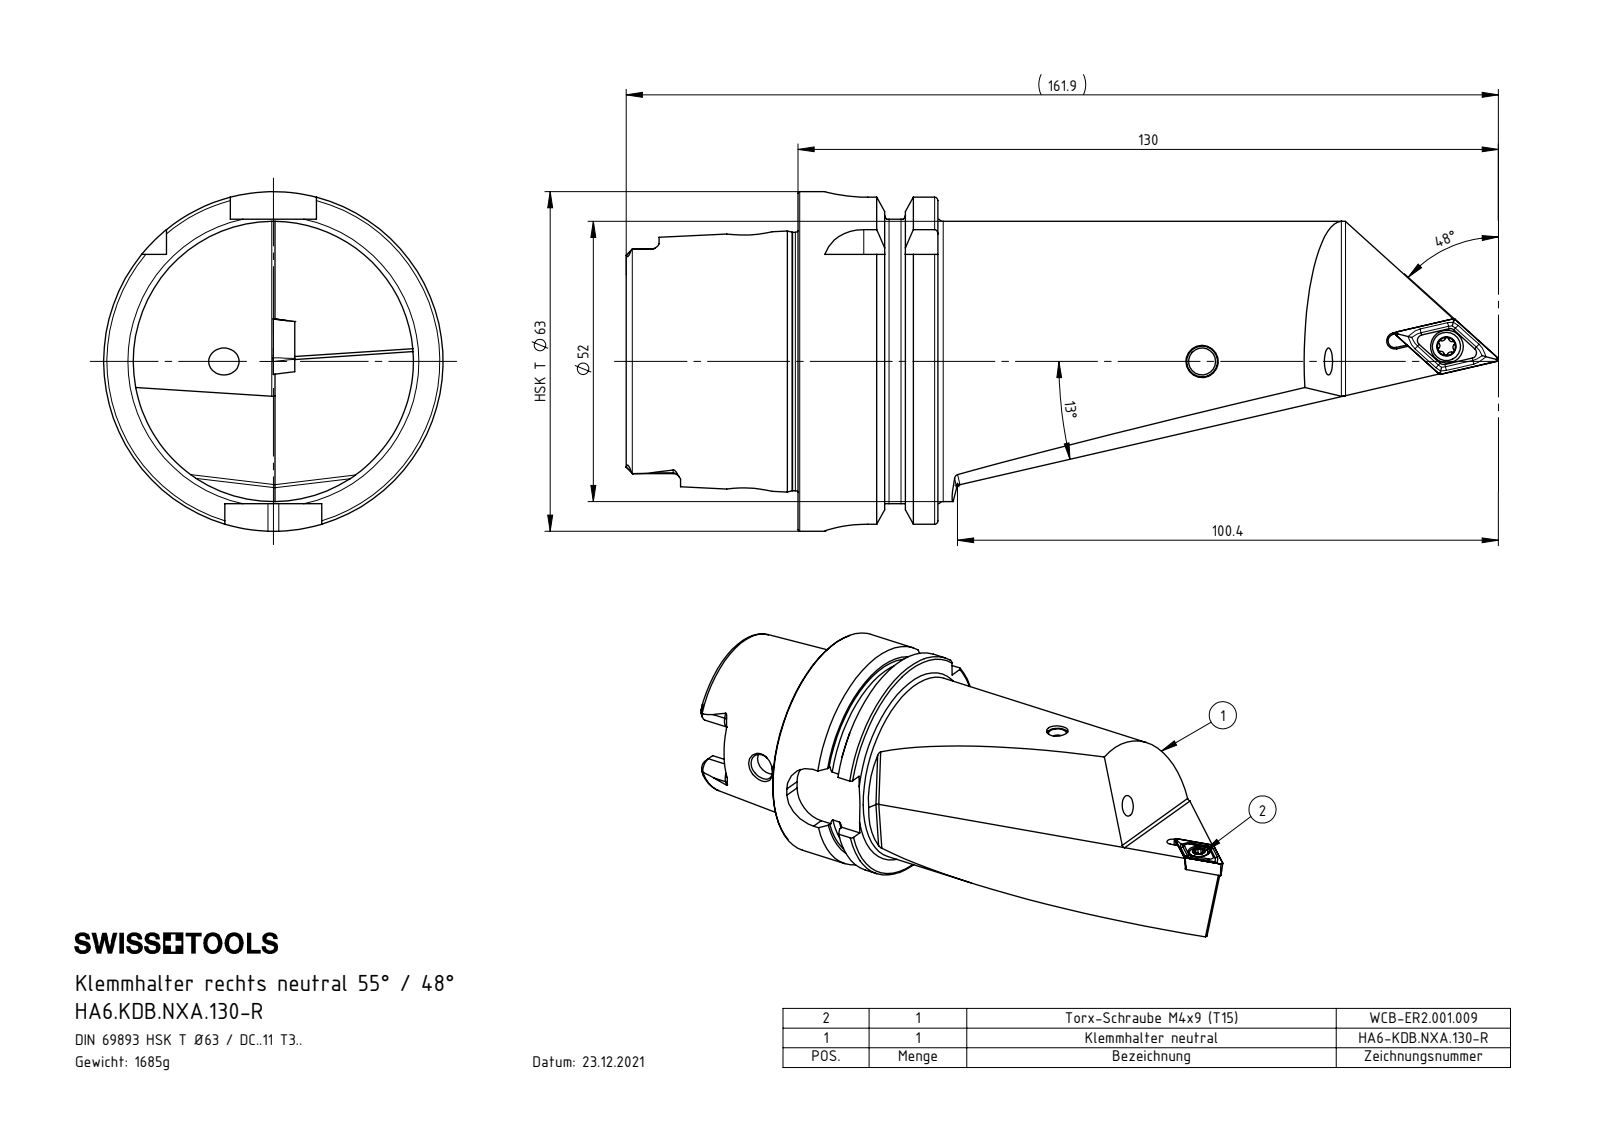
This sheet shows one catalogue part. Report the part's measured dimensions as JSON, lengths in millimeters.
{"part_name": "6-K.B.NXA.130-R; KVT_MB_600_060; DCMT11T304; HA6-KDB.NXA.130-R_A (+1 more)", "step_written_by": "SolidWorks 2017 (AUTOMOTIVE_DESIGN)", "units": "millimeters", "bodies": {"solids": 5, "faces": 303, "planar": 81, "cylindrical": 87, "other": 135}, "overall_size": [161.91, 63, 63], "volume_mm3": 214336, "surface_area_mm2": 37407, "round_holes": [[5, 2], [3.3, 1], [4.4, 1], [6.1, 1], [7.5, 1], [8.4, 1], [10, 1], [17, 1], [19, 1], [34, 1], [40, 1]], "round_bosses_or_shafts": [[63, 1], [54.95, 1], [52, 1], [47.94, 1], [6, 1], [5.25, 1], [4, 1]], "partial_cylinders_radius": [[0.34, 6], [0.59, 6], [1.4, 6], [8, 4], [0.8, 3], [2.82, 2], [2.88, 2], [1.25, 1]], "face_to_face_distances": [25.95, 16, 9.95, 31.9, 41.85, 57.85, 52.8, 21.8, 11.85, 53.7], "hole_center_spacings": [45.45, 45.53, 68, 113.39, 113.48]}
